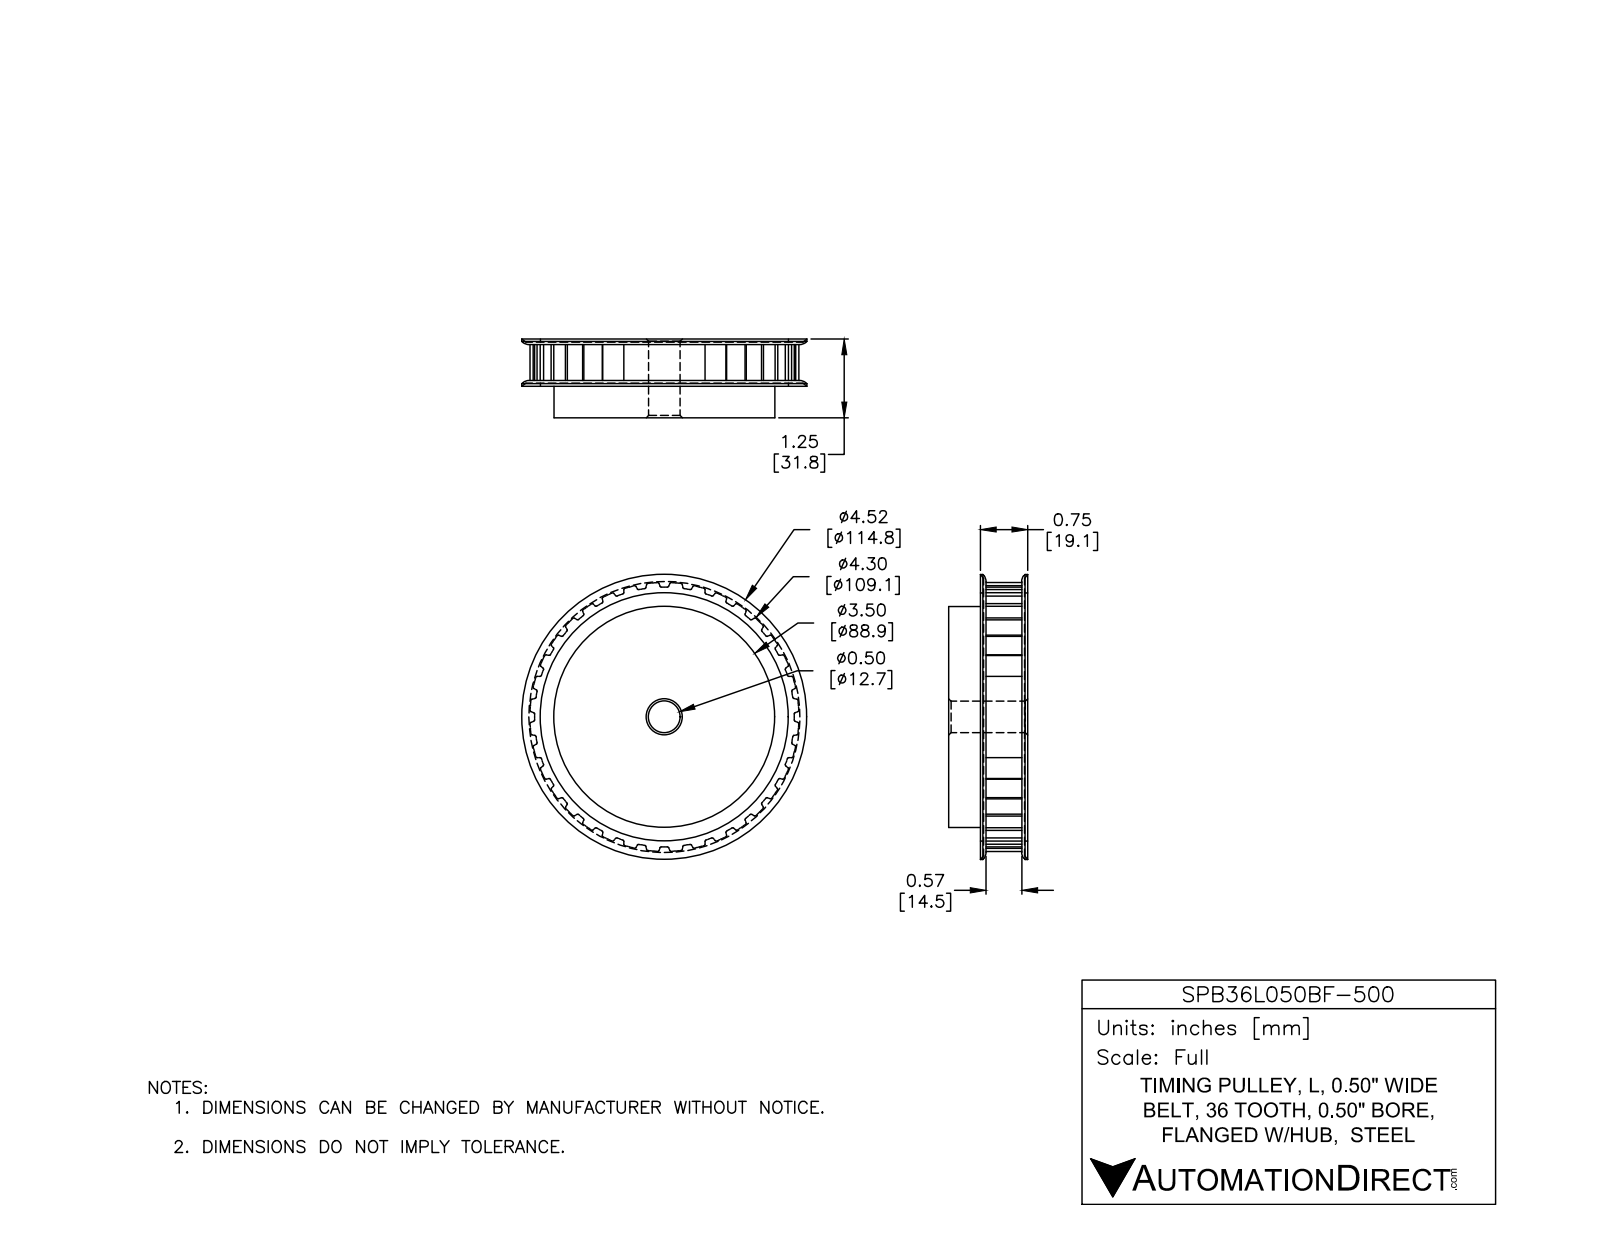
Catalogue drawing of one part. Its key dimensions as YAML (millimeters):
part_name: "SPB36L050BF-500"
step_written_by: "SolidWorks 2015 (AUTOMOTIVE_DESIGN)"
units: millimeters
bodies: {solids: 1, faces: 349, planar: 115, cylindrical: 218, other: 16}
overall_size: [114.8, 114.8, 31.8]
volume: 245300
surface_area: 36190
round_holes:
  - {diameter: 12.7, count: 1}
round_bosses_or_shafts:
  - {diameter: 114.8, count: 1}
  - {diameter: 99.9, count: 1}
  - {diameter: 88.9, count: 1}
partial_cylinders:
  - {radius: 0.5, count: 144}
  - {radius: 54.2, count: 1}
face_to_face_distances: [31.8, 1.3, 17.8, 30.5, 16.5, 14, 19.1, 12.7, 2.3, 16.8]
